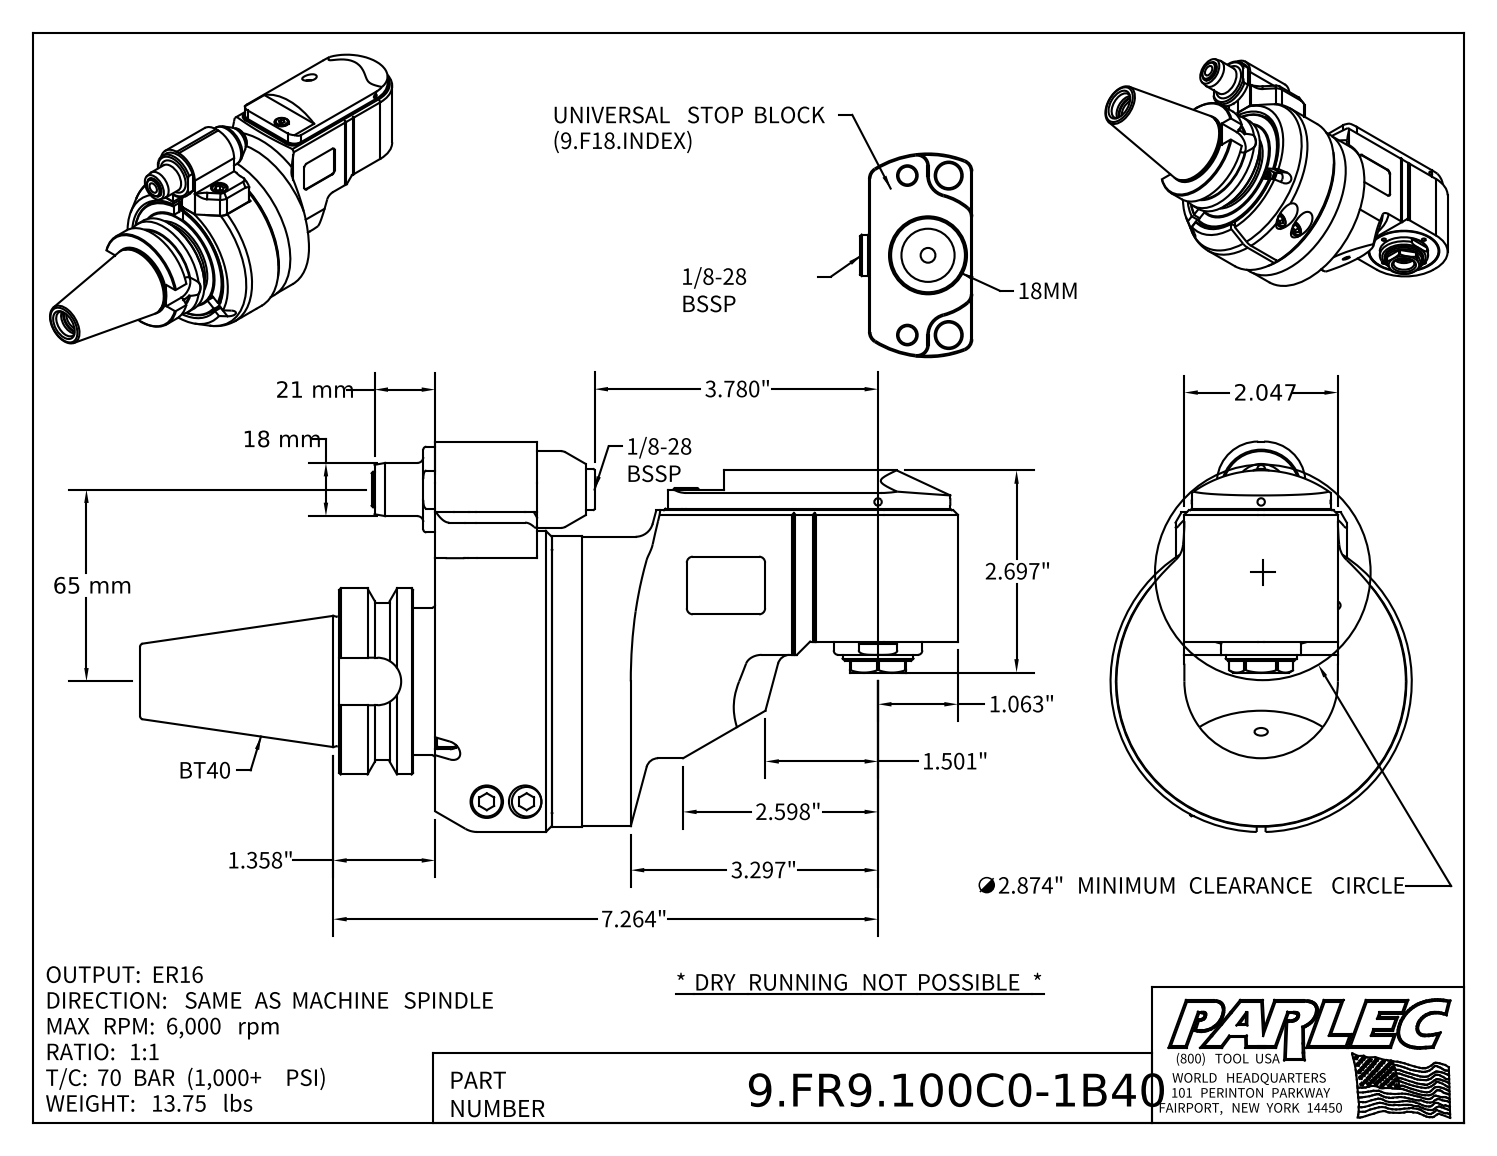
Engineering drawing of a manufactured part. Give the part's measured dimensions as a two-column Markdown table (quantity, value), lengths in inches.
| quantity | value |
| --- | --- |
| part name | 9.FR9.100C0-1B40; 9_FR9_100B0; 9_GA1_346_2 (Type 1, BT40, 65mm) |
| STEP written by | Autodesk Inventor 2022 (AUTOMOTIVE_DESIGN) |
| units | inches |
| bodies | 5 solids, 633 faces (283 planar, 176 cylindrical, 174 other) |
| overall size | 10.902 × 5.206 × 4.016 |
| volume | 62.18 in³ |
| surface area | 256.6 in² |
| round holes (diameter × count) | 0.335 × 22, 0.102 × 10, 0.197 × 7, 0.098 × 3, 0.118 × 3, 0.433 × 3, 0.165 × 2, 0.354 × 2, 0.409 × 2, 0.512 × 2, 0.13 × 1, 0.177 × 1 |
| round bosses / shafts (diameter × count) | 0.394 × 4, 0.236 × 4, 0.709 × 2, 0.335 × 2, 0.315 × 2, 0.098 × 2, 4.016 × 1, 3.874 × 1 |
| partial cylindrical surfaces (radius × count) | 0.079 × 12, 0.157 × 4, 0.02 × 2, 0.039 × 2, 0.138 × 2, 0.197 × 2, 0.236 × 2, 0.551 × 2 |
| main face-to-face distances | 1.555, 0.335, 0.295, 1.26, 1.083, 2.047, 0.039, 1.22, 0.02, 0.276 |
| hole center spacings | 1.496, 2.973, 2.992, 0.339, 0.382, 0.435, 0.689, 0.974 |
